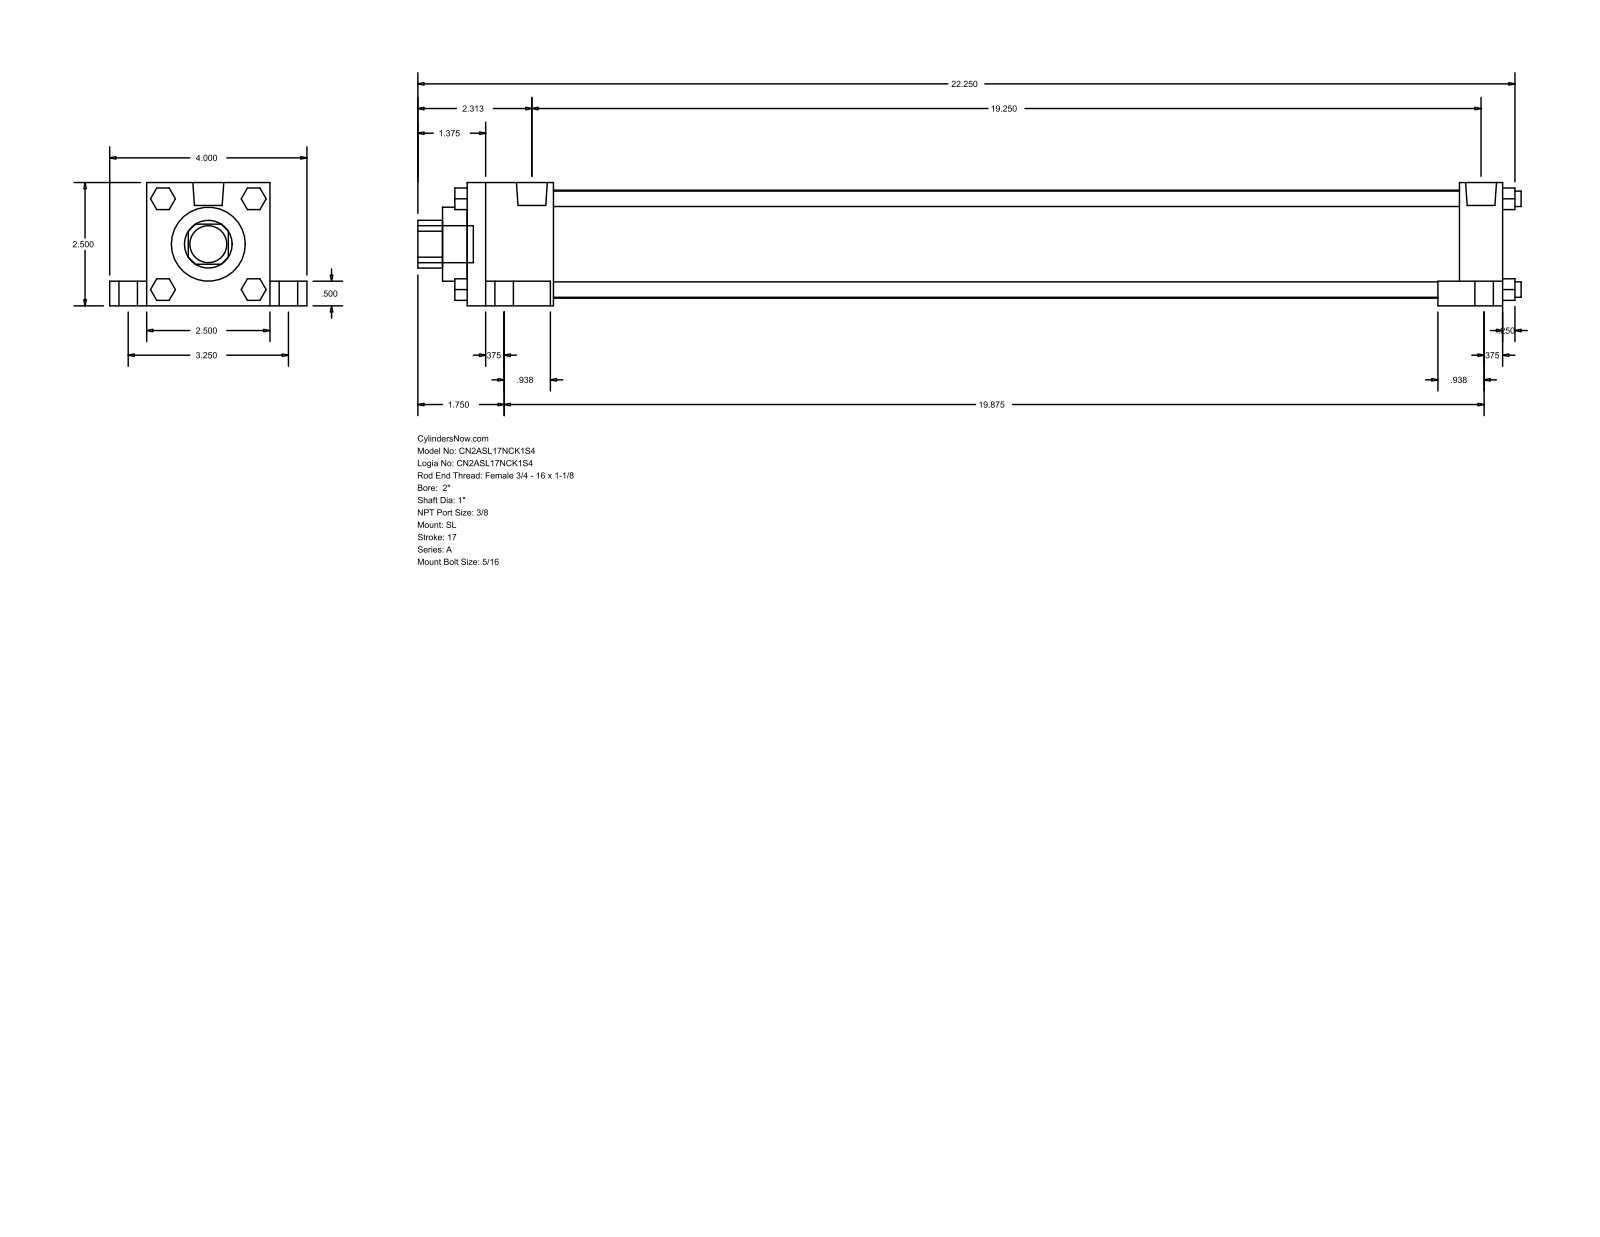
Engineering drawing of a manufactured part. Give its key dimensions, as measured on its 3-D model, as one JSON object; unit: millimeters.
{"part_name": "A_SL__0200_1", "step_written_by": "GSSL Pune (CONFIG_CONTROL_DESIGN)", "units": "millimeters", "bodies": {"solids": 0, "faces": 148, "planar": 112, "cylindrical": 36, "other": 0}, "overall_size": [568.33, 101.6, 63.5], "round_holes": [[25.4, 1], [38.1, 1], [55.63, 1]], "round_bosses_or_shafts": [[15.88, 4], [9.53, 4], [7.94, 4], [5.56, 4], [15.93, 2], [19.05, 1]], "partial_cylinders_radius": [[12.29, 1]], "face_to_face_distances": [63.5, 12.7, 533.4, 50.8, 22.22, 19.05, 82.55, 44.45, 488.95, 511.18]}
